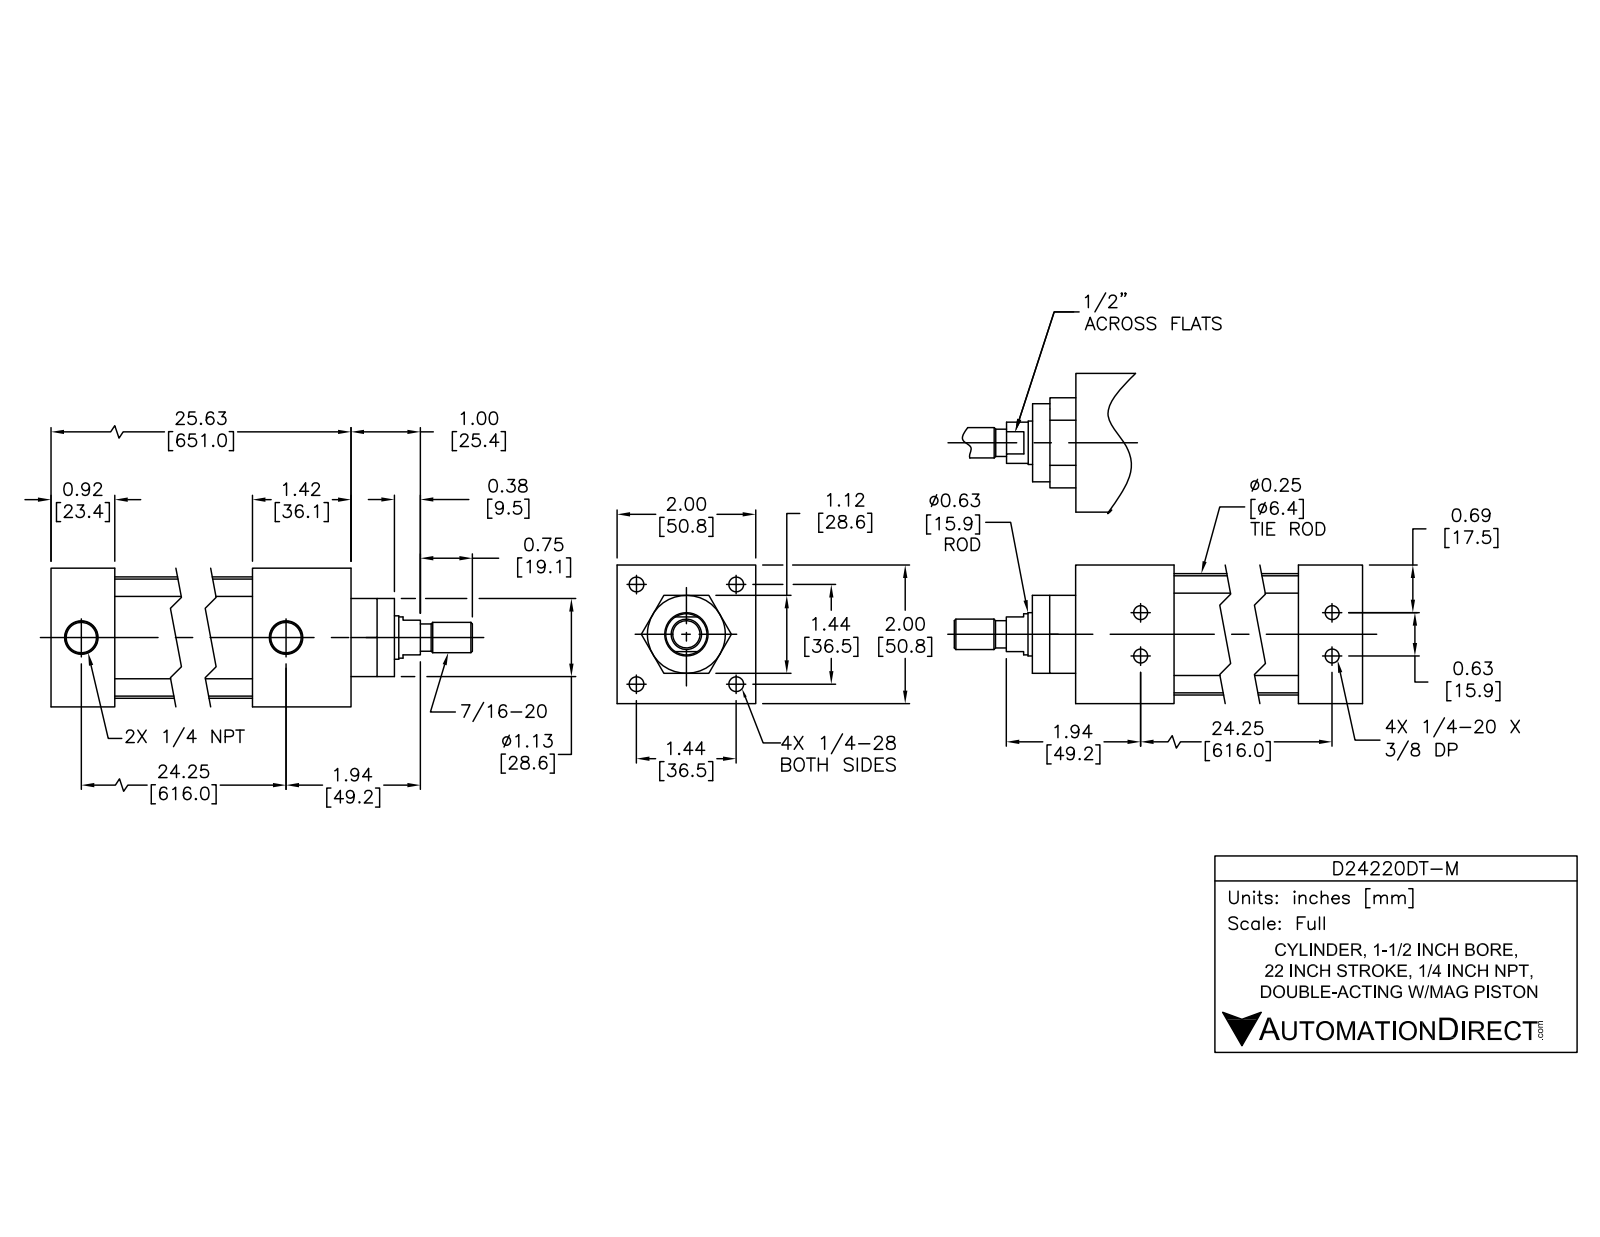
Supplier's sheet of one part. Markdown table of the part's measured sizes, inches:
| quantity | value |
| --- | --- |
| part name | D24220DT-M BODY; D24220DT-M PISTON; D24220DT-M |
| STEP written by | SolidWorks 2015 (AUTOMOTIVE_DESIGN) |
| units | inches |
| bodies | 12 solids, 303 faces (99 planar, 114 cylindrical, 90 other) |
| overall size | 27.371 × 2 × 2 |
| volume | 36.82 in³ |
| surface area | 422.1 in² |
| round holes (diameter × count) | 0.196 × 4, 0.211 × 4, 0.281 × 4, 0.406 × 4, 0.297 × 2, 0.477 × 2, 0.625 × 1, 0.628 × 1, 1.5 × 1 |
| round bosses / shafts (diameter × count) | 0.39 × 4, 0.25 × 4, 0.222 × 4, 1.75 × 1, 1.497 × 1, 1.121 × 1, 0.622 × 1, 0.59 × 1 |
| partial cylindrical surfaces (radius × count) | 0.2 × 4 |
| main face-to-face distances | 2, 25.621, 1.42, 24.201, 24.701, 23.281, 0.92, 1.121, 24.601, 23.181 |
| hole center spacings | 0.312, 0.313, 0.625, 1.014, 1.014, 1.434, 1.434, 2.028 |
